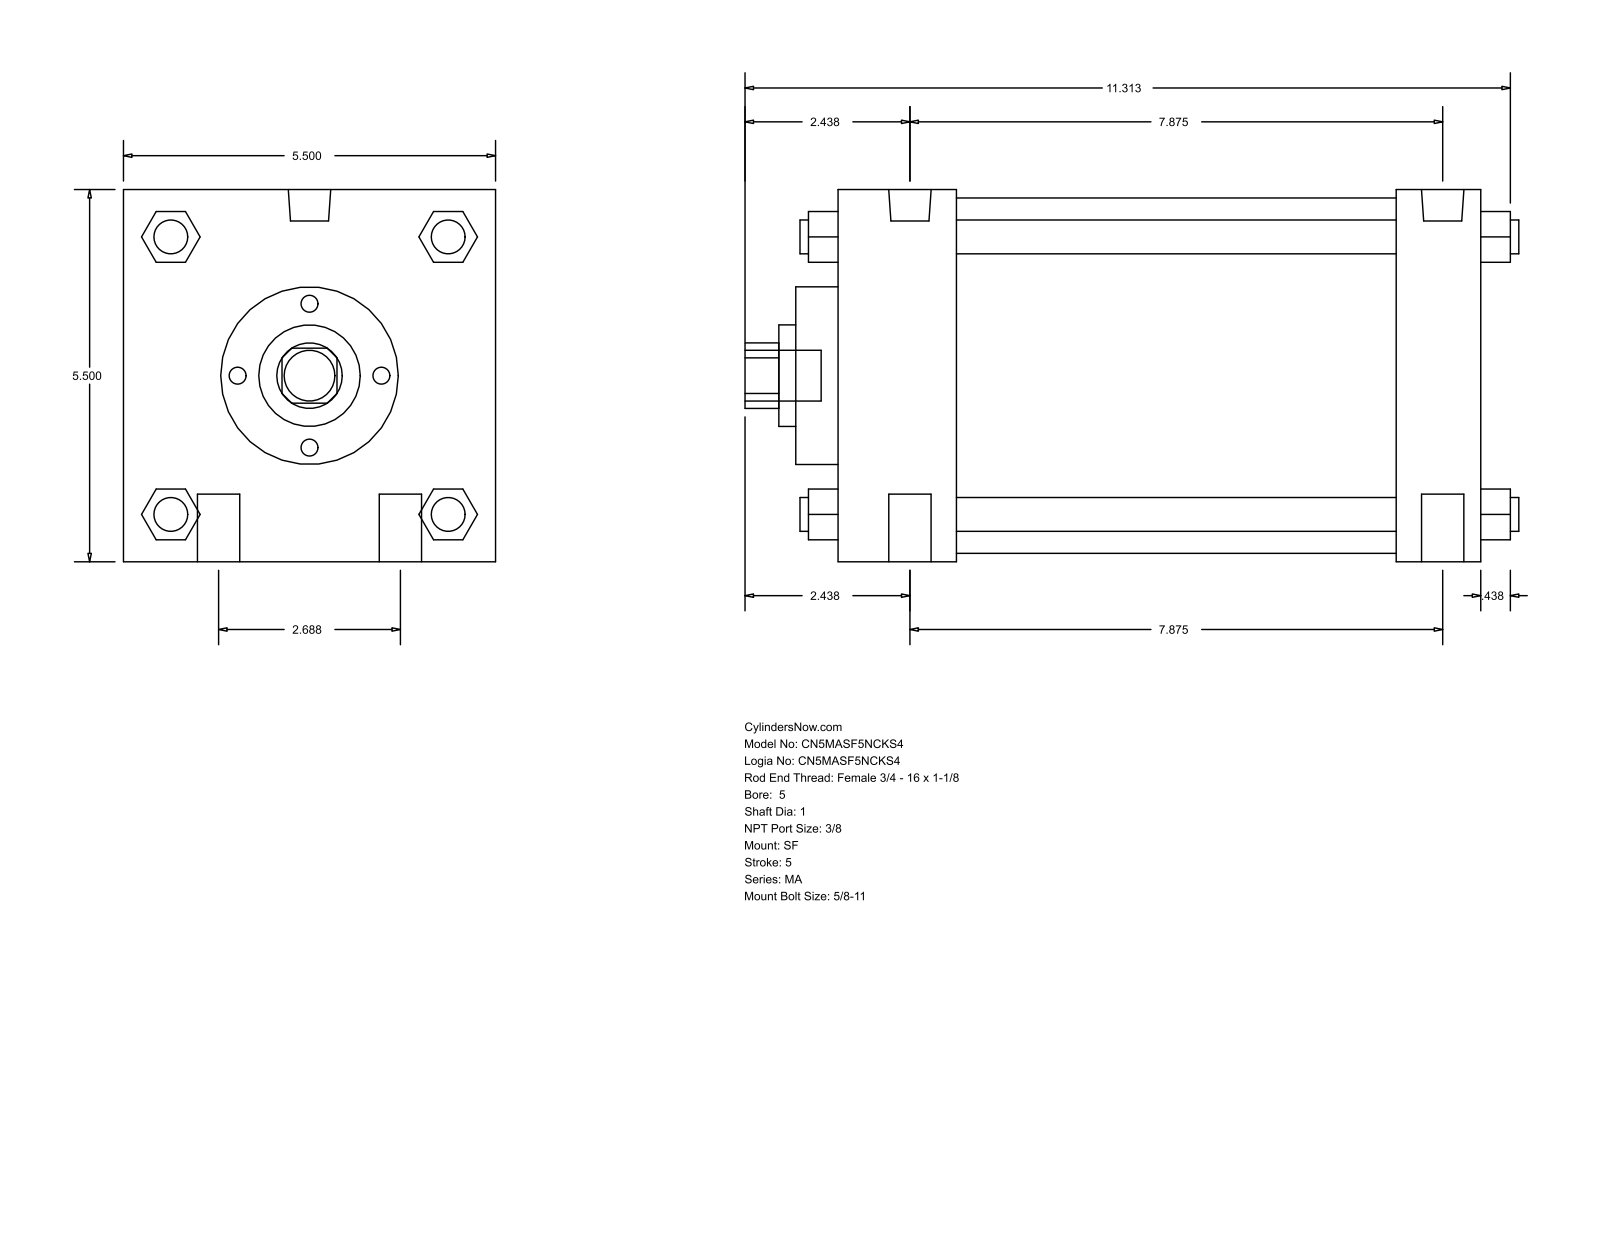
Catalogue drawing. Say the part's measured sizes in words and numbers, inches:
The part is named "MA_SF__0500_1". Its 3-D file was written by "GSSL Pune (CONFIG_CONTROL_DESIGN)". It is 0 solids with 126 faces: 95 planar, 31 cylindrical and 0 other. Overall it measures 11.437 by 5.5 by 5.5 inches. Round holes: 1 of diameter 1, 1 of diameter 1.5, 1 of diameter 2.625, 1 of diameter 5.25. Round bosses or shafts: 4 of diameter 0.625, 4 of diameter 0.5, 2 of diameter 0.627, 2 of diameter 0.437, 1 of diameter 0.75. Partial cylindrical surfaces (rounded edges, fillets, slot ends): 1 of radius 0.484. The main face-to-face distances are 5.5, 9.5, 1.75, 8.25, 6.5, 7.75, 1.25, 0.625, 2.375, 8.875.
